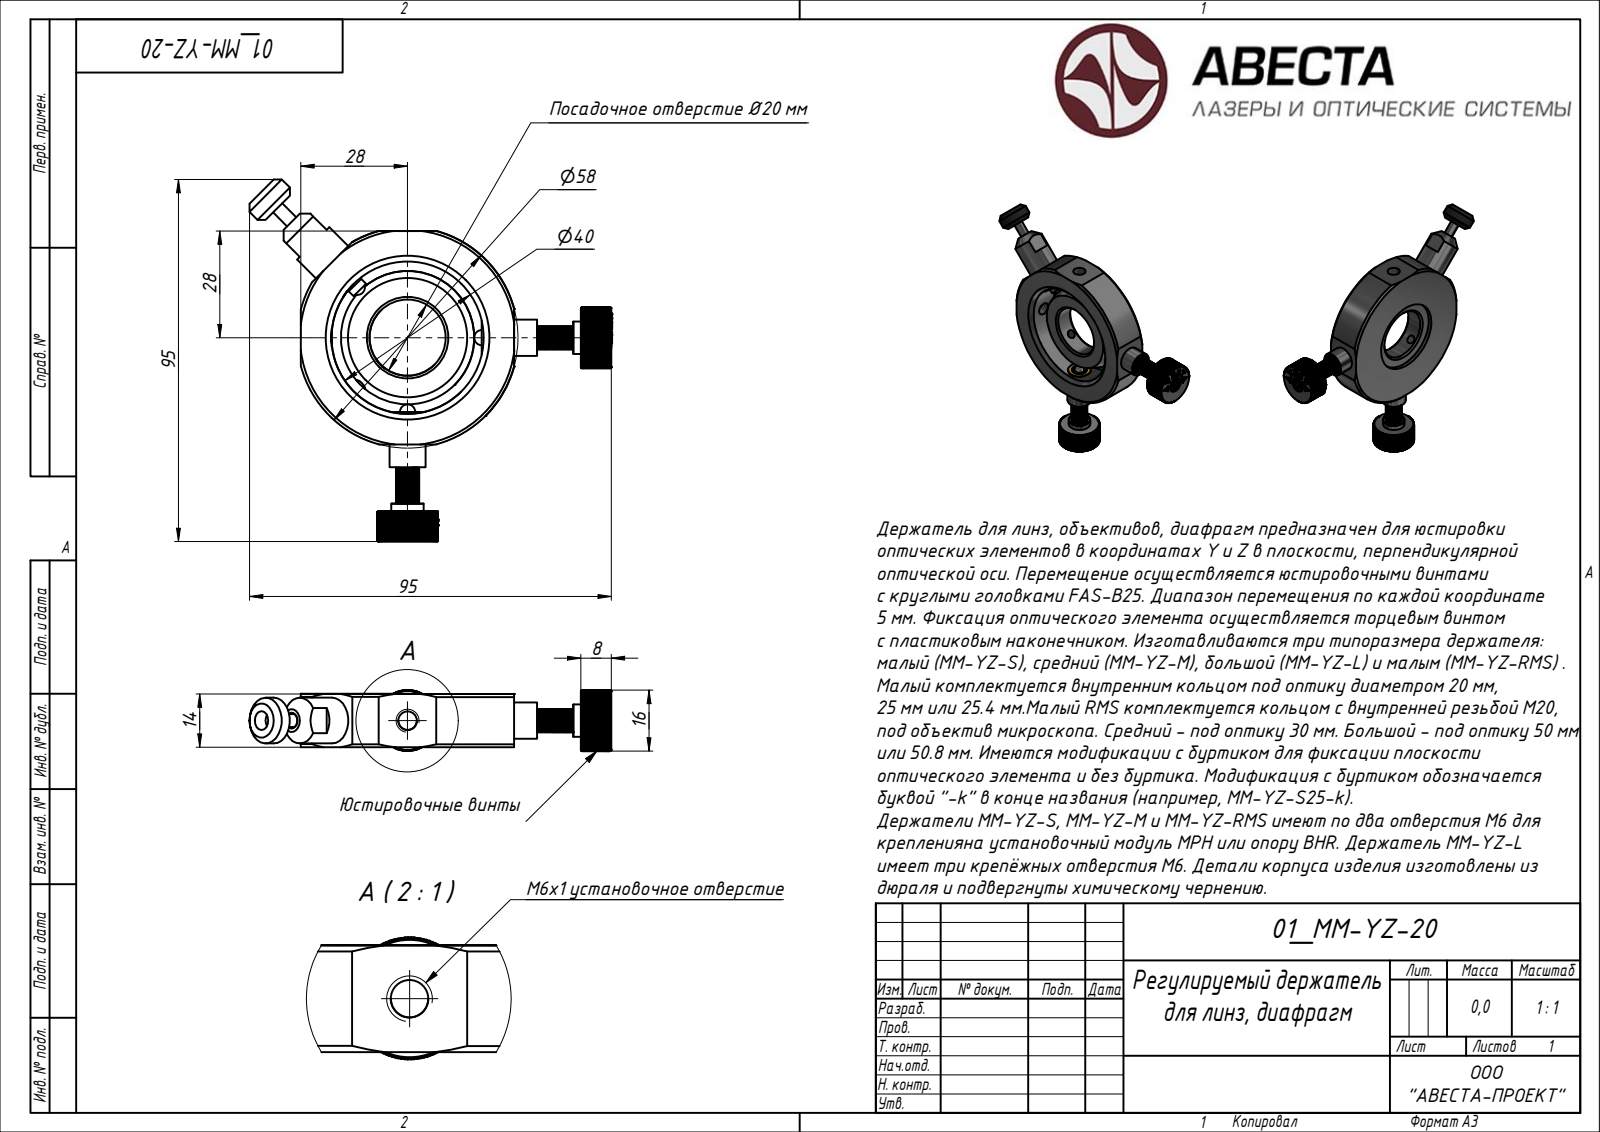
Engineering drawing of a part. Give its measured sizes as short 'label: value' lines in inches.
name: 01_MM-YZ-25.4; 01_MM-YZ-25
written by: ST-DEVELOPER v15 (AUTOMOTIVE_DESIGN)
unit: in
bodies: 42 solids, 1734 faces (790 planar, 0 cylindrical, 944 other)
size: 11.061 × 3.814 × 0.635
volume: 5.428 in³; area: 88.07 in²
face distances: 0.315, 0.059, 0.492, 0.493, 0.551, 0.059, 0.06, 0.058, 0.552, 0.491
